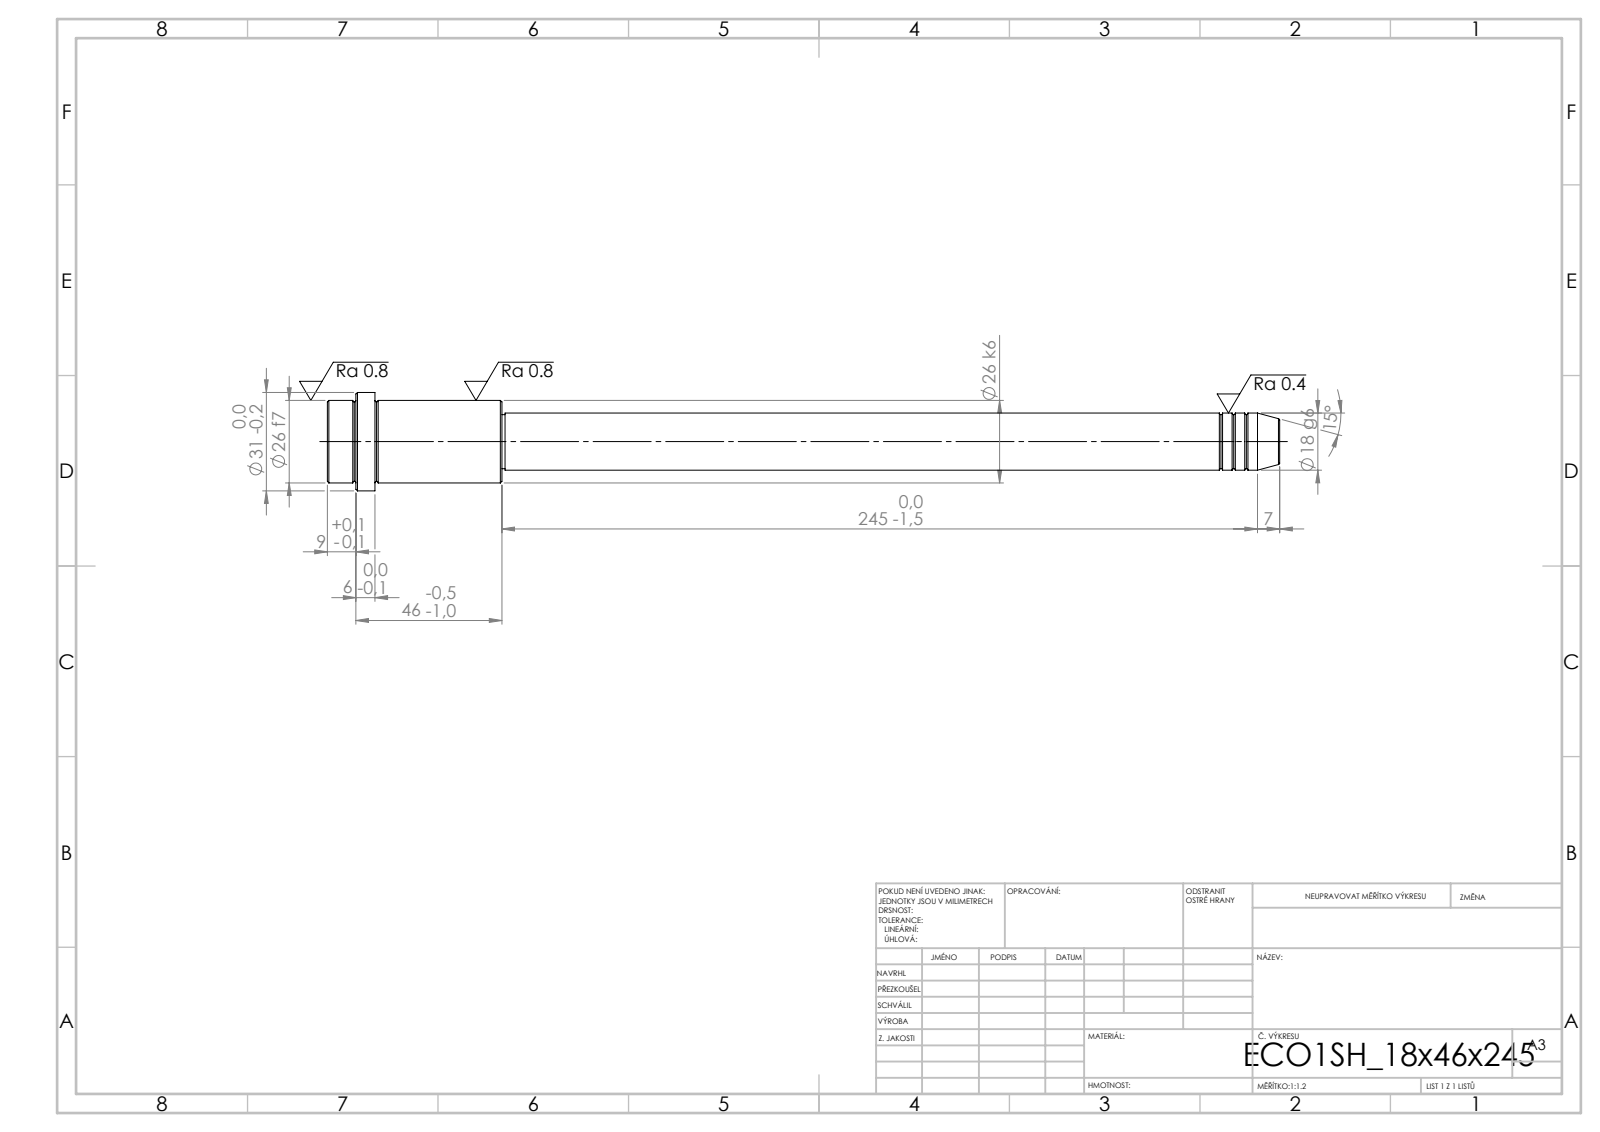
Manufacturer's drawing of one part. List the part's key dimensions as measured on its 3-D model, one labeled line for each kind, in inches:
STEP written by: SolidWorks 2019 (CONFIG_CONTROL_DESIGN)
Units: inches
Bodies: 1 solid, 52 faces (6 planar, 16 cylindrical, 30 other)
Overall size (bounding box): 11.811 × 1.22 × 1.22
Volume: 5.636 in³ · Surface area: 30.96 in²
Round bosses / shafts (diameter × count): ⌀1.22 ×1, ⌀1.024 ×1, ⌀0.709 ×1, ⌀0.669 ×1
Main face-to-face distances: 2.165, 1.575, 0.591, 1.811, 0.236, 0.354, 9.646, 11.22, 11.457, 11.811
